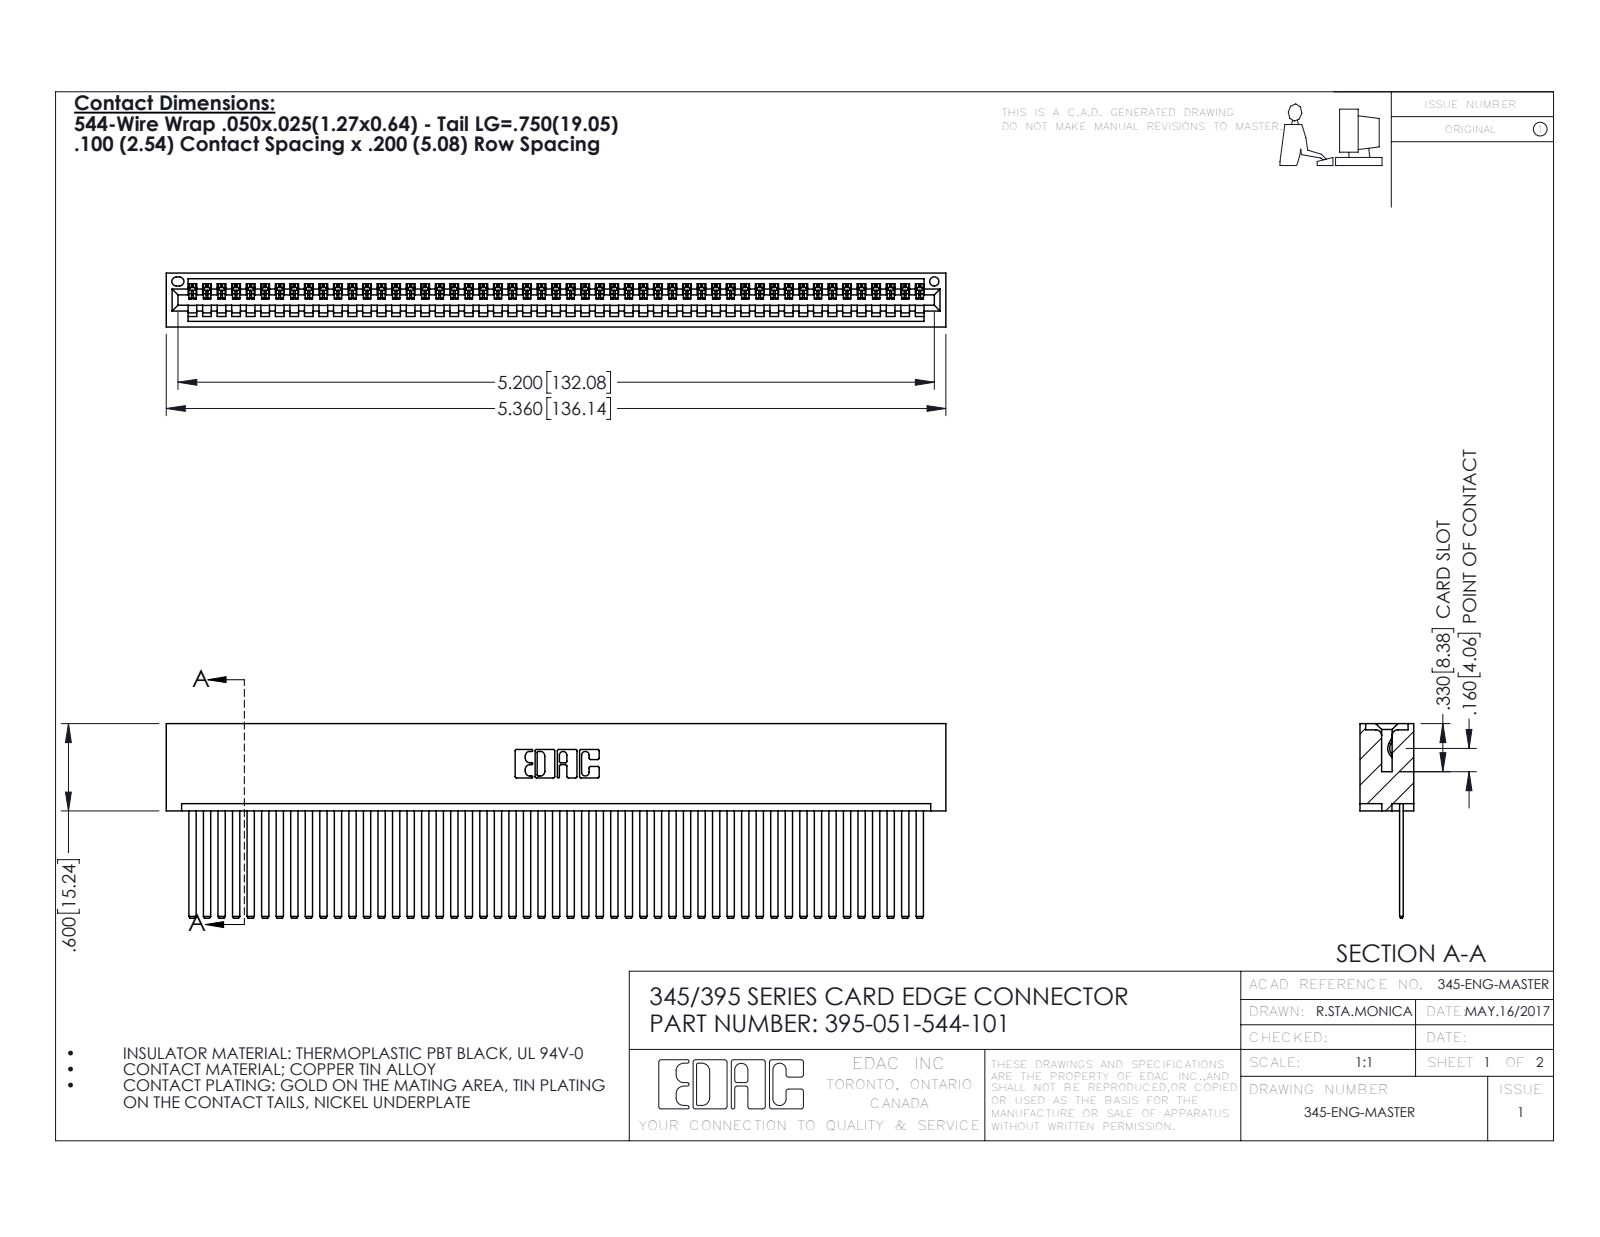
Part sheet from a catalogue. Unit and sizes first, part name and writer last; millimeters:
Units: millimetres
Overall size (bounding box): 136.1 × 34 × 9.4
Round holes (diameter × count): ⌀1.6 ×1
Partial cylindrical surfaces — rounded edges, fillets, slot ends (radius × count): R0.2 ×102, R0.3 ×22, R0.2 ×6, R0.8 ×6, R0.7 ×3, R0.8 ×2, R1 ×2, R0.4 ×1
Main face-to-face distances: 1.8, 7.6, 0.6, 2.5, 6.9, 9.4, 5.1, 5.7, 3.8, 1.8
Volume: 14 200 mm³ · Surface area: 20 930 mm²
Bodies: 52 solids, 2770 faces (1912 planar, 858 cylindrical, 0 other)
Part name (STEP PRODUCT): 395-051-544-101; 345-292-001_345-293-144; 345 Part_No Mounting Lugs
STEP written by: SolidWorks 2016 (CONFIG_CONTROL_DESIGN)
